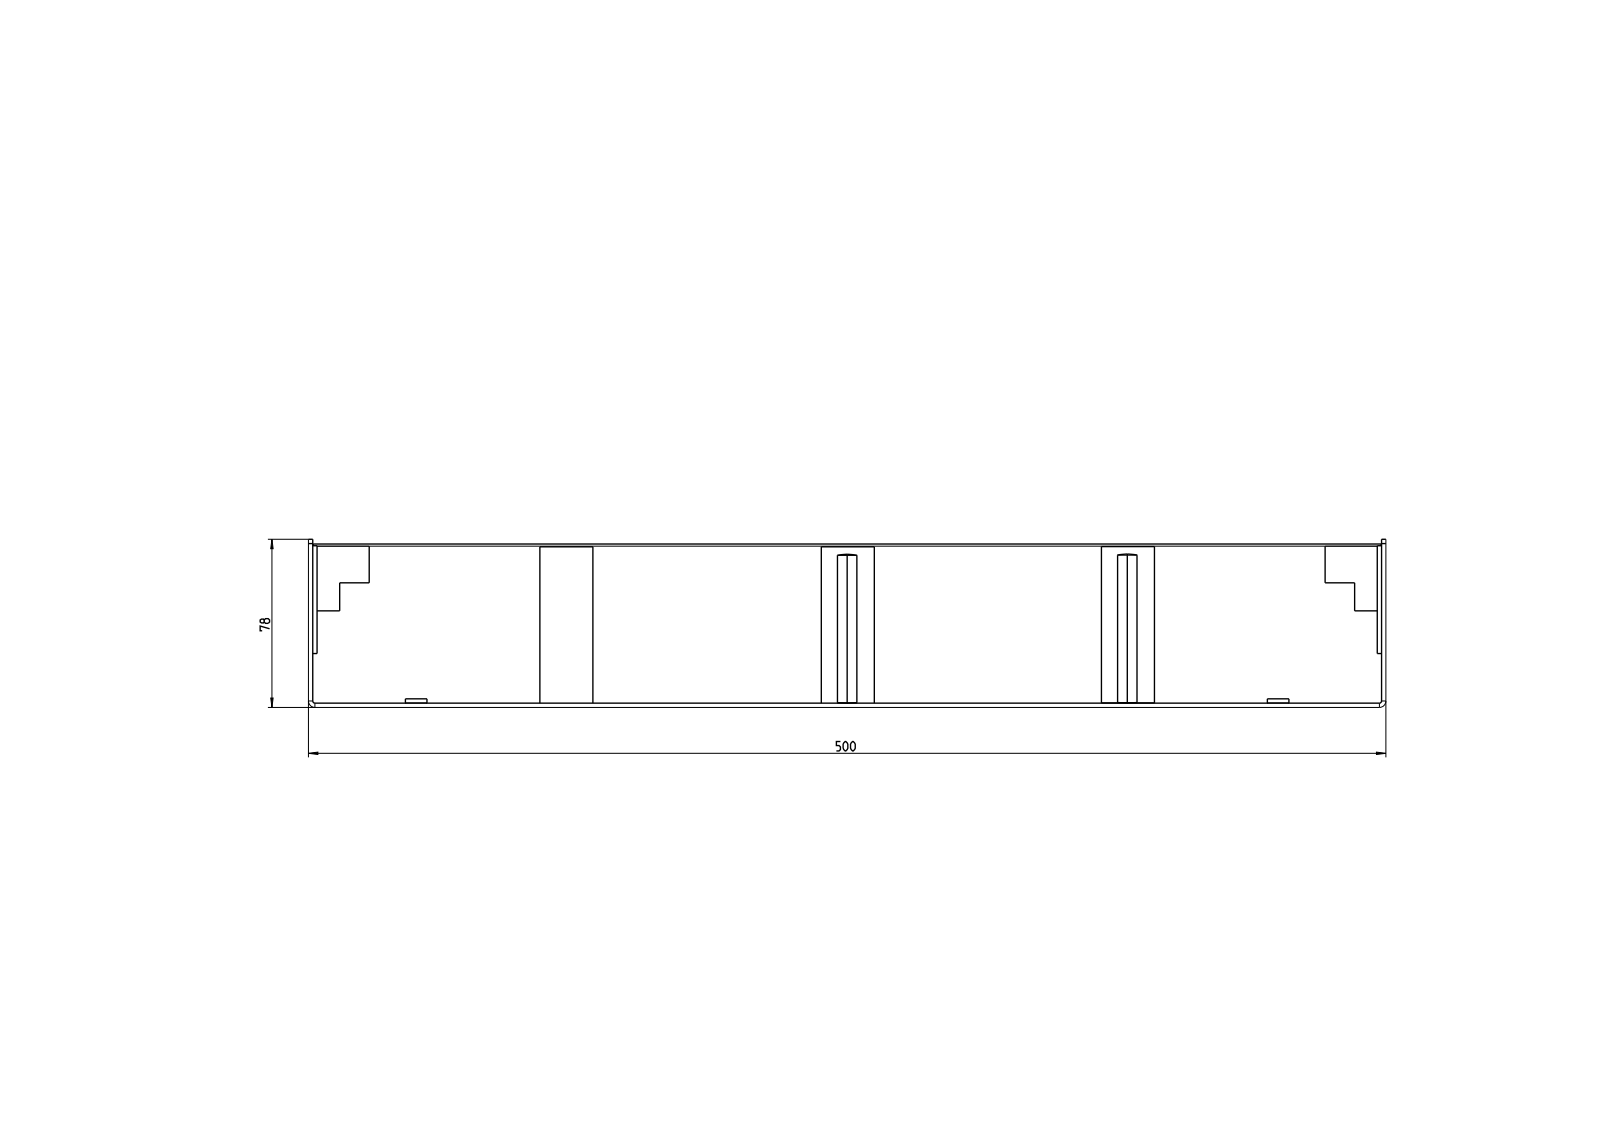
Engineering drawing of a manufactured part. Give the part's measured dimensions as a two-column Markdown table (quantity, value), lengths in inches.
| quantity | value |
| --- | --- |
| part name | T-01023; T-01024; T-01025_AF0; T-01026_ASM (+8 more) |
| STEP written by | CREO PARAMETRIC BY PTC INC, 2022024 (AUTOMOTIVE_DESIGN) |
| units | inches |
| bodies | 20 solids, 665 faces (490 planar, 117 cylindrical, 58 other) |
| overall size | 78.74 × 19.685 × 3.08 |
| volume | 737.2 in³ |
| surface area | 10 140 in² |
| round holes (diameter × count) | 0.535 × 13, 0.236 × 8, 0.335 × 8 |
| round bosses / shafts (diameter × count) | 0.394 × 8 |
| partial cylindrical surfaces (radius × count) | 0.004 × 26, 0.039 × 2, 0.118 × 2 |
| main face-to-face distances | 0.079, 2.866, 2.906, 0.039, 2.945, 2.984, 19.528, 19.449, 0.157, 19.606 |
| hole center spacings | 23.622, 28.39, 0.787, 15.748, 15.768, 31.496, 47.244, 49.8 |
